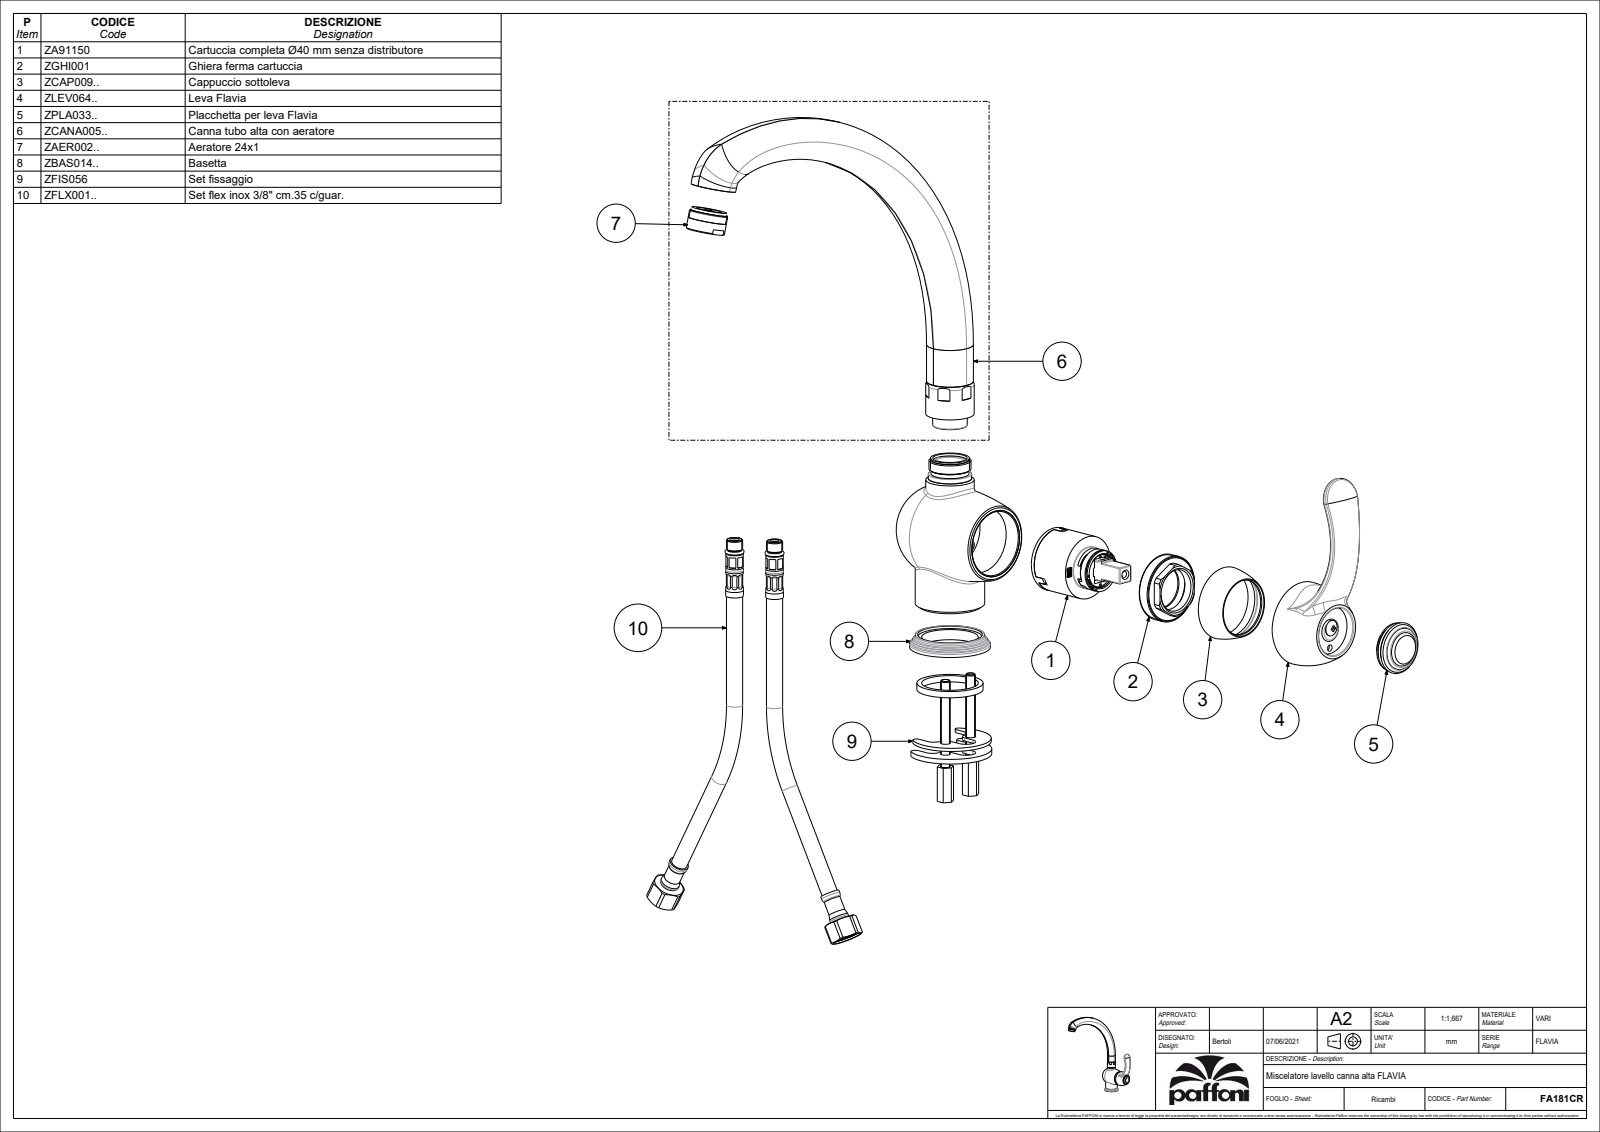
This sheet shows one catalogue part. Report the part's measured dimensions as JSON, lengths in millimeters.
{"part_name": "FA181CR", "step_written_by": "CREO PARAMETRIC BY PTC INC, 2020044 (CONFIG_CONTROL_DESIGN)", "units": "millimeters", "bodies": {"solids": 3, "faces": 2706, "planar": 2042, "cylindrical": 337, "other": 327}, "overall_size": [305.2, 249.54, 125.43], "volume_mm3": 249188, "surface_area_mm2": 139155, "round_holes": [[8, 4], [7, 3], [11, 3], [4, 2], [5.25, 2], [6.5, 2], [9, 2], [11.7, 2], [21, 2], [21.2, 2], [3.5, 1], [5, 1]], "round_bosses_or_shafts": [[24, 2], [50, 1], [46.5, 1], [43, 1], [39.5, 1], [37.4, 1], [36.7, 1], [32.1, 1]], "partial_cylinders_radius": [[0.5, 45], [0.2, 24], [1.5, 4], [1, 1], [3.25, 1], [5.25, 1], [7, 1], [10.05, 1]], "face_to_face_distances": [2.5, 6.5, 0.5, 58.3, 39.4, 5, 41.9, 18.9, 6, 3], "hole_center_spacings": [13.04, 13.46, 0.54, 1.51, 2, 7.77, 8.6, 8.7]}
